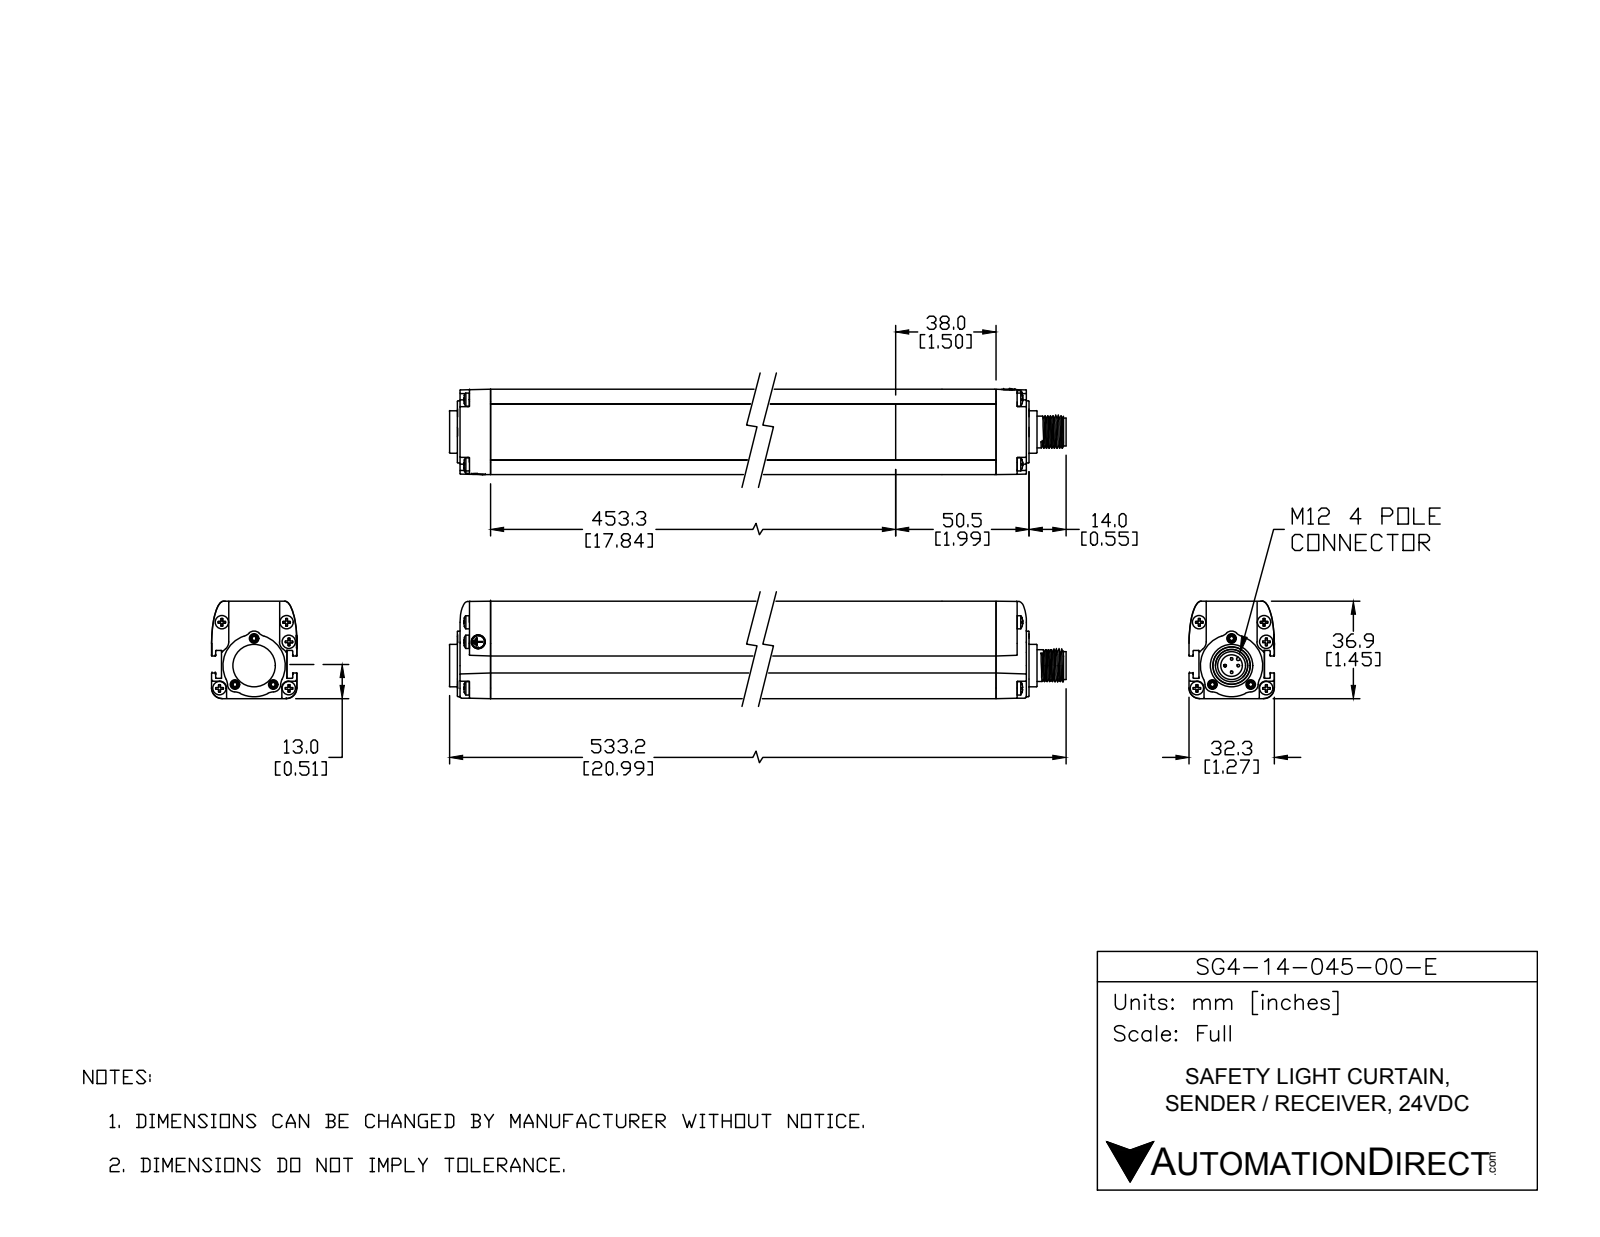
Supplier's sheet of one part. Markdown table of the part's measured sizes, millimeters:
| quantity | value |
| --- | --- |
| part name | SG4-14-045-OO-E |
| STEP written by | SolidWorks 2017 (AUTOMOTIVE_DESIGN) |
| units | millimeters |
| bodies | 29 solids, 1708 faces (410 planar, 623 cylindrical, 675 other) |
| overall size | 533.2 × 63 × 52.2 |
| volume | 546 700 mm³ |
| surface area | 141 400 mm² |
| round holes (diameter × count) | 2.7 × 6, 5.3 × 6, 2.1 × 4, 4.2 × 4, 6.6 × 4, 1.5 × 3, 3.6 × 3, 8.2 × 1, 9.6 × 1, 11 × 1, 14.3 × 1 |
| round bosses / shafts (diameter × count) | 5 × 10, 10 × 4, 1 × 4, 4.7 × 2, 16 × 1, 14 × 1, 12 × 1, 10.5 × 1 |
| partial cylindrical surfaces (radius × count) | 0.2 × 148, 0.1 × 120, 0.2 × 18, 2.7 × 18, 3 × 8, 5 × 7, 2.8 × 3, 0.4 × 2 |
| main face-to-face distances | 2, 32.3, 3.8, 36.3, 28.5, 34.3, 4, 3, 24.7, 8.5 |
| hole center spacings | 14.5, 451.3, 10.2, 6.1, 7.4, 13.2, 13.7, 15.7 |
